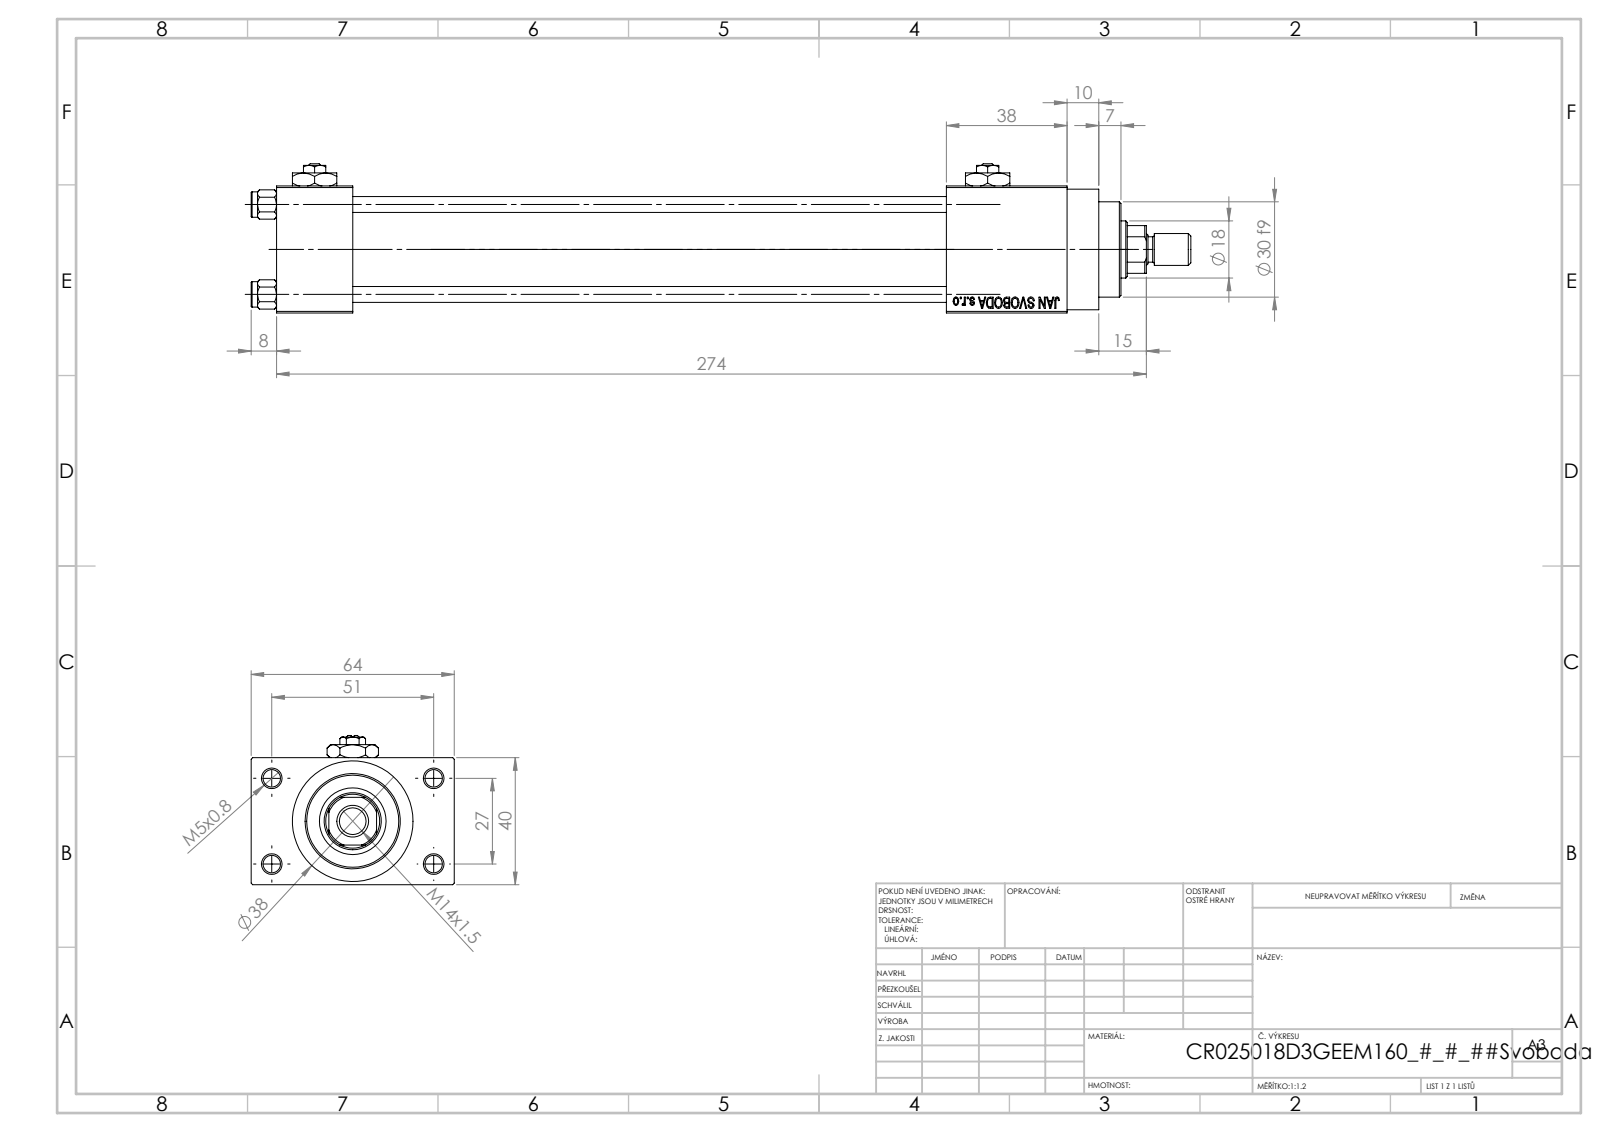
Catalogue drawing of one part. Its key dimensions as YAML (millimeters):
part_name: "V215CR_D_Body; V215_VC_A; NUT_M5_D; V215CR_VCP_D (+3 more)"
step_written_by: "SolidWorks 2019 (CONFIG_CONTROL_DESIGN)"
units: millimeters
bodies: {solids: 14, faces: 1213, planar: 545, cylindrical: 102, other: 566}
overall_size: [296, 64, 47]
volume: 264360
surface_area: 107818
round_holes:
  - {diameter: 5, count: 4}
  - {diameter: 5.5, count: 4}
  - {diameter: 20, count: 3}
  - {diameter: 7, count: 2}
  - {diameter: 13.16, count: 2}
  - {diameter: 8.5, count: 1}
  - {diameter: 18, count: 1}
  - {diameter: 21, count: 1}
  - {diameter: 25, count: 1}
  - {diameter: 30, count: 1}
round_bosses_or_shafts:
  - {diameter: 8, count: 5}
  - {diameter: 38, count: 1}
  - {diameter: 31, count: 1}
  - {diameter: 10, count: 1}
partial_cylinders:
  - {radius: 8.5, count: 1}
face_to_face_distances: [40, 12, 52, 187, 24, 211, 64, 38, 225, 249]
hole_center_spacings: [11.37, 20.01, 28.3, 28.85, 29.89, 39.66, 48.34, 27]
